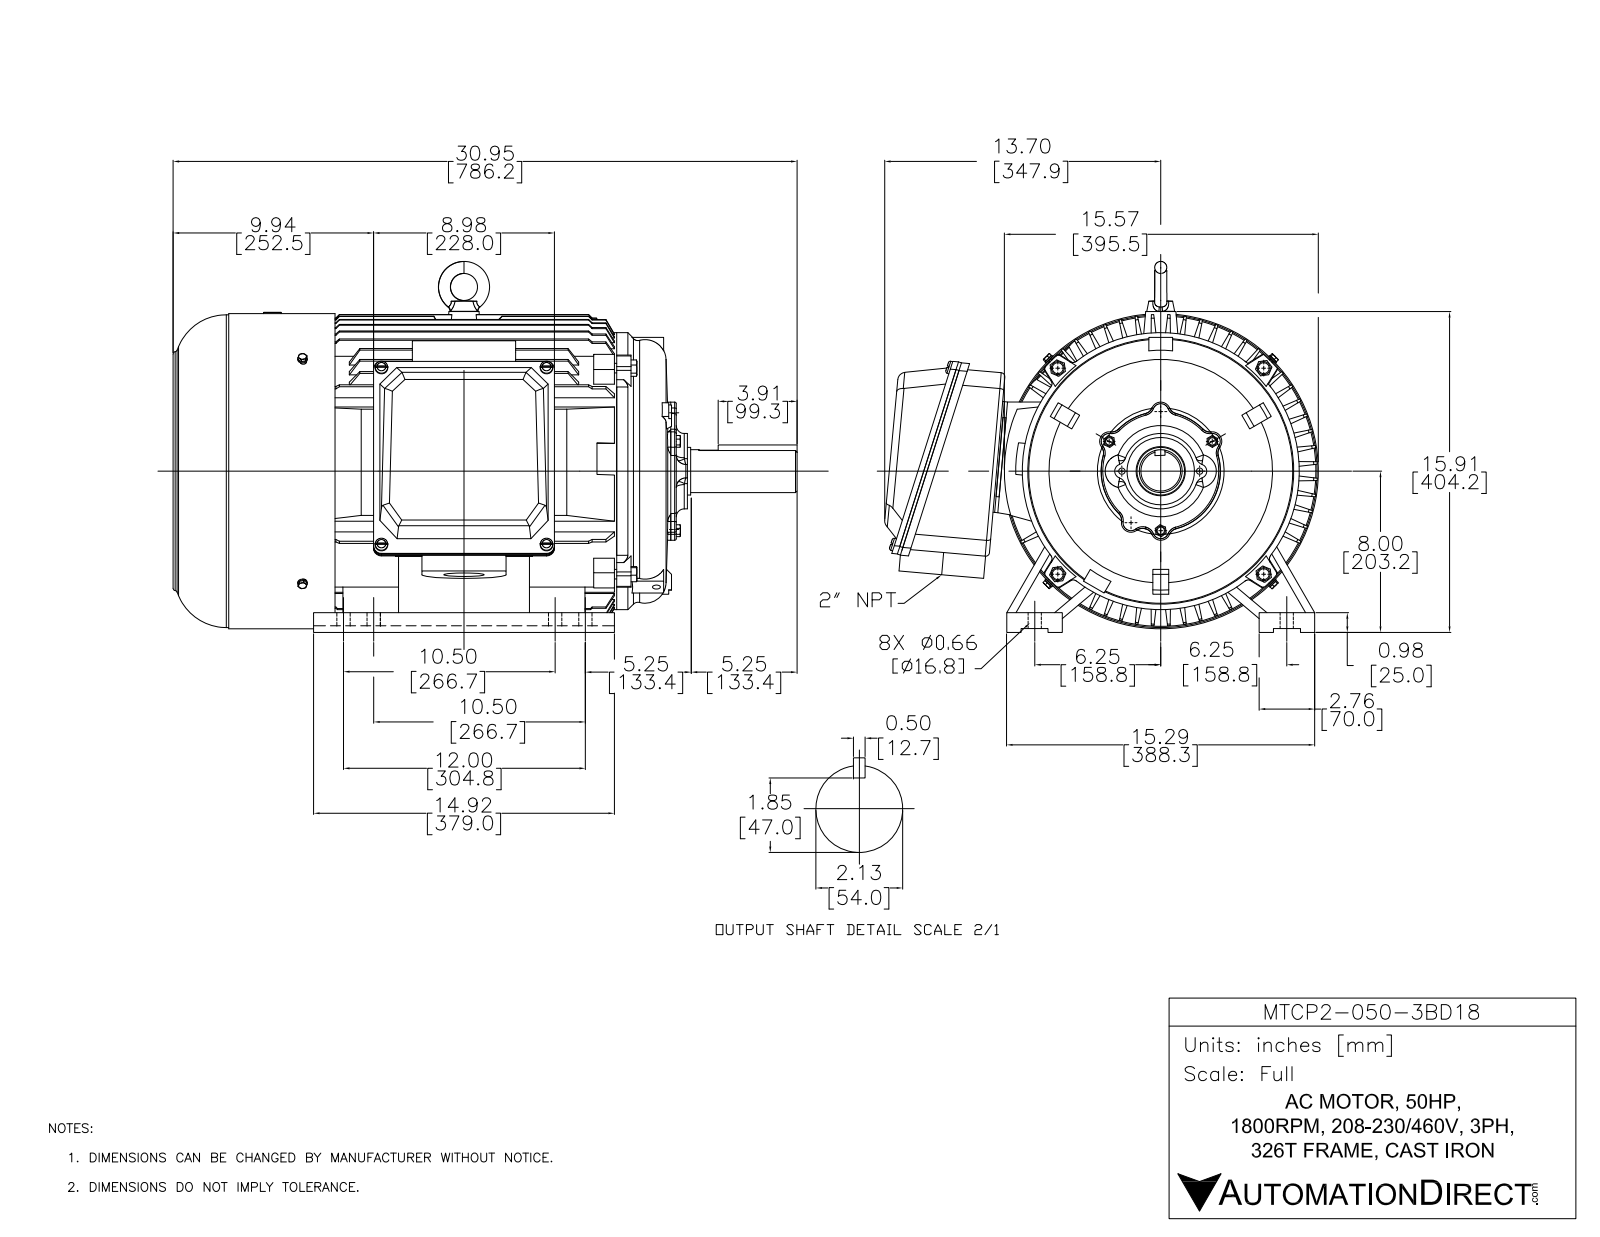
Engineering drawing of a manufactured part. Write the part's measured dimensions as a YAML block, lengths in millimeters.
part_name: "PEWWE-326T-4,6,8"
step_written_by: "SolidWorks 2017 (AUTOMOTIVE_DESIGN)"
units: millimeters
bodies: {solids: 31, faces: 3013, planar: 2012, cylindrical: 568, other: 433}
overall_size: [786.15, 546.4, 467.4]
volume: 18410000
surface_area: 3636000
round_holes:
  - {diameter: 10, count: 22}
  - {diameter: 17, count: 8}
  - {diameter: 8, count: 6}
  - {diameter: 6.4, count: 4}
  - {diameter: 6.8, count: 4}
  - {diameter: 12, count: 4}
  - {diameter: 12.2, count: 4}
  - {diameter: 13.7, count: 4}
  - {diameter: 15, count: 4}
  - {diameter: 9.2, count: 3}
  - {diameter: 19, count: 2}
  - {diameter: 10.1, count: 1}
round_bosses_or_shafts:
  - {diameter: 12, count: 4}
  - {diameter: 6, count: 4}
  - {diameter: 7.19, count: 3}
  - {diameter: 10.86, count: 2}
  - {diameter: 10.86, count: 2}
  - {diameter: 397, count: 1}
  - {diameter: 394, count: 1}
  - {diameter: 349, count: 1}
partial_cylinders:
  - {radius: 12, count: 32}
  - {radius: 10, count: 20}
  - {radius: 4, count: 15}
  - {radius: 5, count: 8}
  - {radius: 8, count: 8}
  - {radius: 20, count: 4}
  - {radius: 9, count: 2}
  - {radius: 37.5, count: 1}
face_to_face_distances: [4, 1.5, 10, 5, 12, 2, 28.62, 20, 25, 86.5]
hole_center_spacings: [100, 75, 38.1, 89.59, 141.42, 144.89, 259.51, 266.7]
